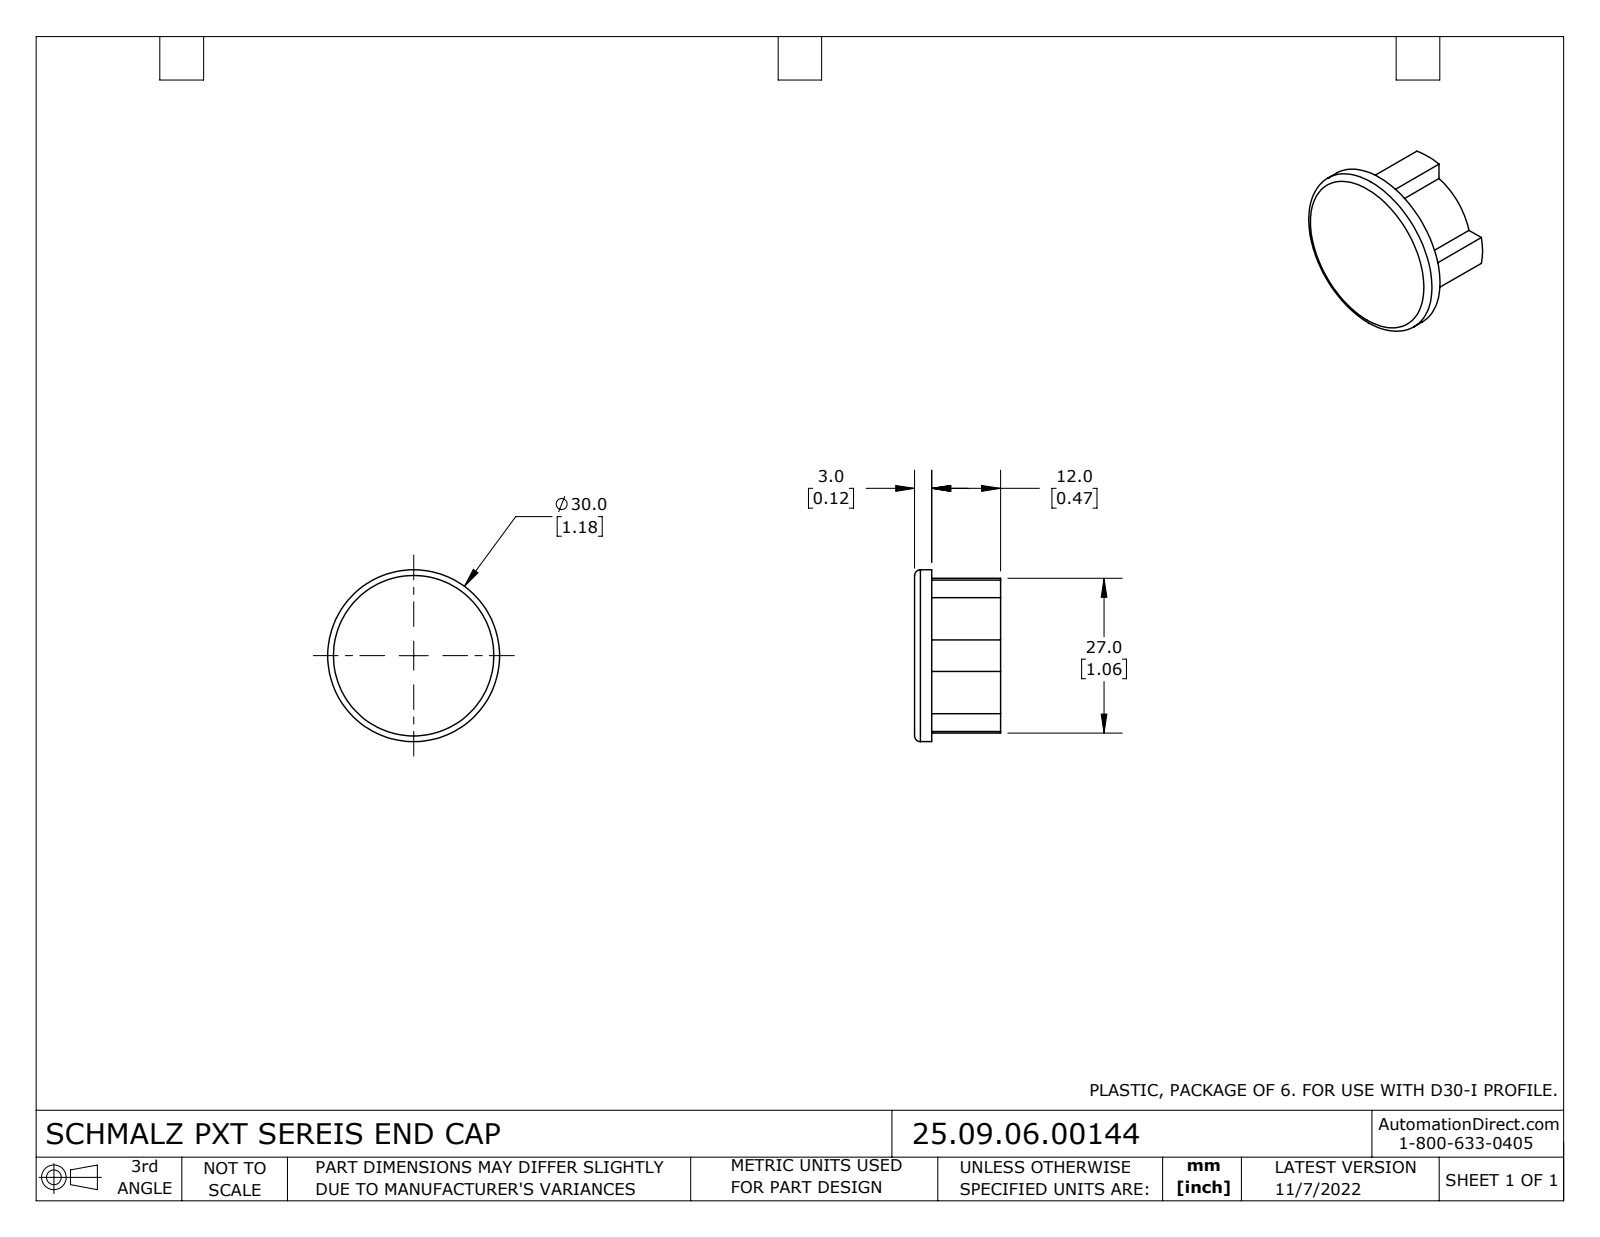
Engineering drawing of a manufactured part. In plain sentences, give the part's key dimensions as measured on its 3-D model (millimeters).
The part is named "25.09.06.00144". Its 3-D file was written by "SolidWorks 2021 (CONFIG_CONTROL_DESIGN)". It is 1 solid with 27 faces: 12 planar, 13 cylindrical and 2 other. Overall it measures 30 by 30 by 15 millimeters. Its volume is 3 654 cubic millimeters and its surface area 3 458 square millimeters. Round holes: 1 of diameter 19. Round bosses or shafts: 1 of diameter 30. Partial cylindrical surfaces (rounded edges, fillets, slot ends): 1 of radius 10.5, 1 of radius 13.5. The main face-to-face distances are 3, 5.5, 15, 12.
